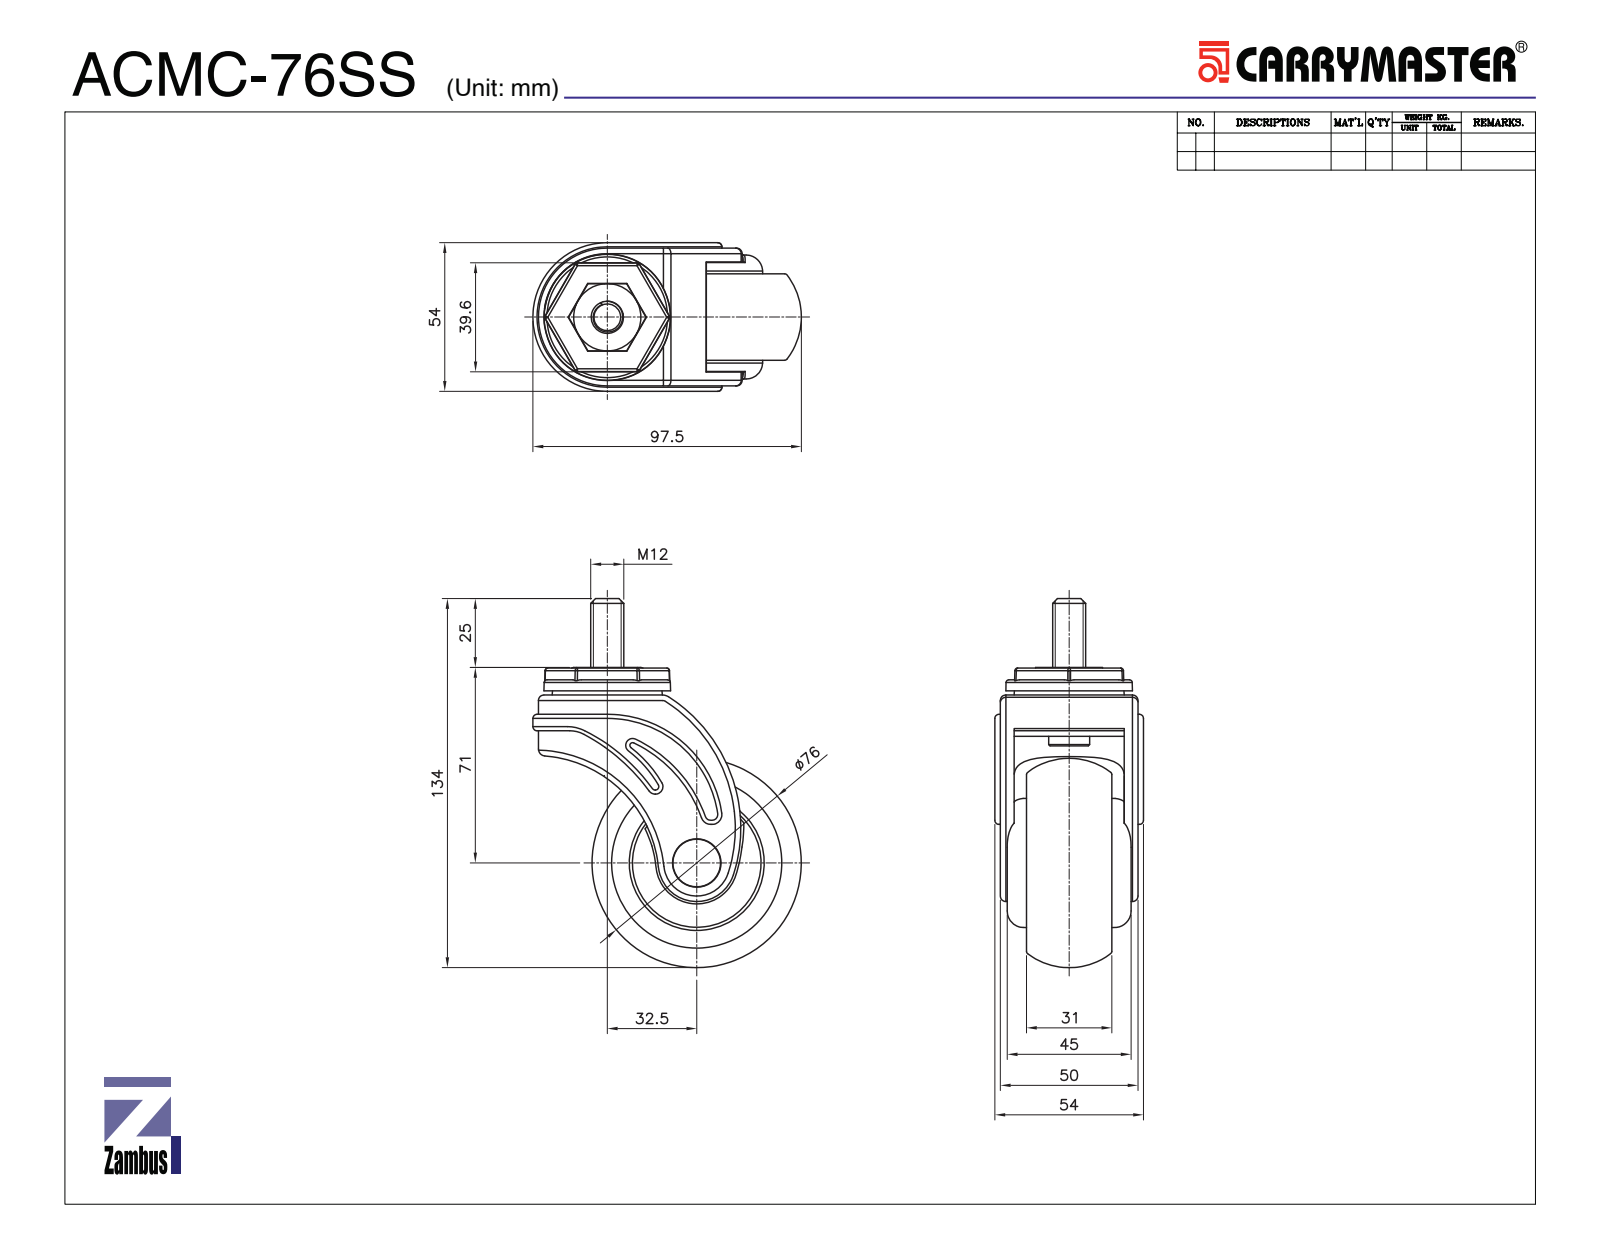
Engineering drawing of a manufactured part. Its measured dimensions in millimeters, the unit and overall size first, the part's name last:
Units: millimetres
Overall size (bounding box): 134 × 97.5 × 54
Round holes (diameter × count): ⌀17.3 ×1, ⌀32.7 ×1, ⌀50 ×1, ⌀62.01 ×1
Round bosses / shafts (diameter × count): ⌀62 ×1, ⌀46.85 ×1, ⌀40 ×1, ⌀21 ×1, ⌀18 ×1, ⌀17 ×1, ⌀10.25 ×1
Partial cylindrical surfaces — rounded edges, fillets, slot ends (radius × count): R1 ×15, R1.5 ×2, R2 ×2, R3.6 ×2, R45 ×2, R2.75 ×1, R2.75 ×1, R4 ×1
Main face-to-face distances: 5, 40, 45, 9.5, 35.5, 4.5, 40.5, 50, 7, 31
Volume: 218 667 mm³ · Surface area: 47 589 mm²
Bodies: 4 solids, 279 faces (69 planar, 129 cylindrical, 81 other)
Part name (STEP PRODUCT): ACMC-76 NON BRAKE FRAME; ACMC-76 S TOP PLATE; ACMC-76 WHEEL; ACMC-76 F TOP PLATE COVER (+1 more)
STEP written by: SolidWorks 2019 (CONFIG_CONTROL_DESIGN)
